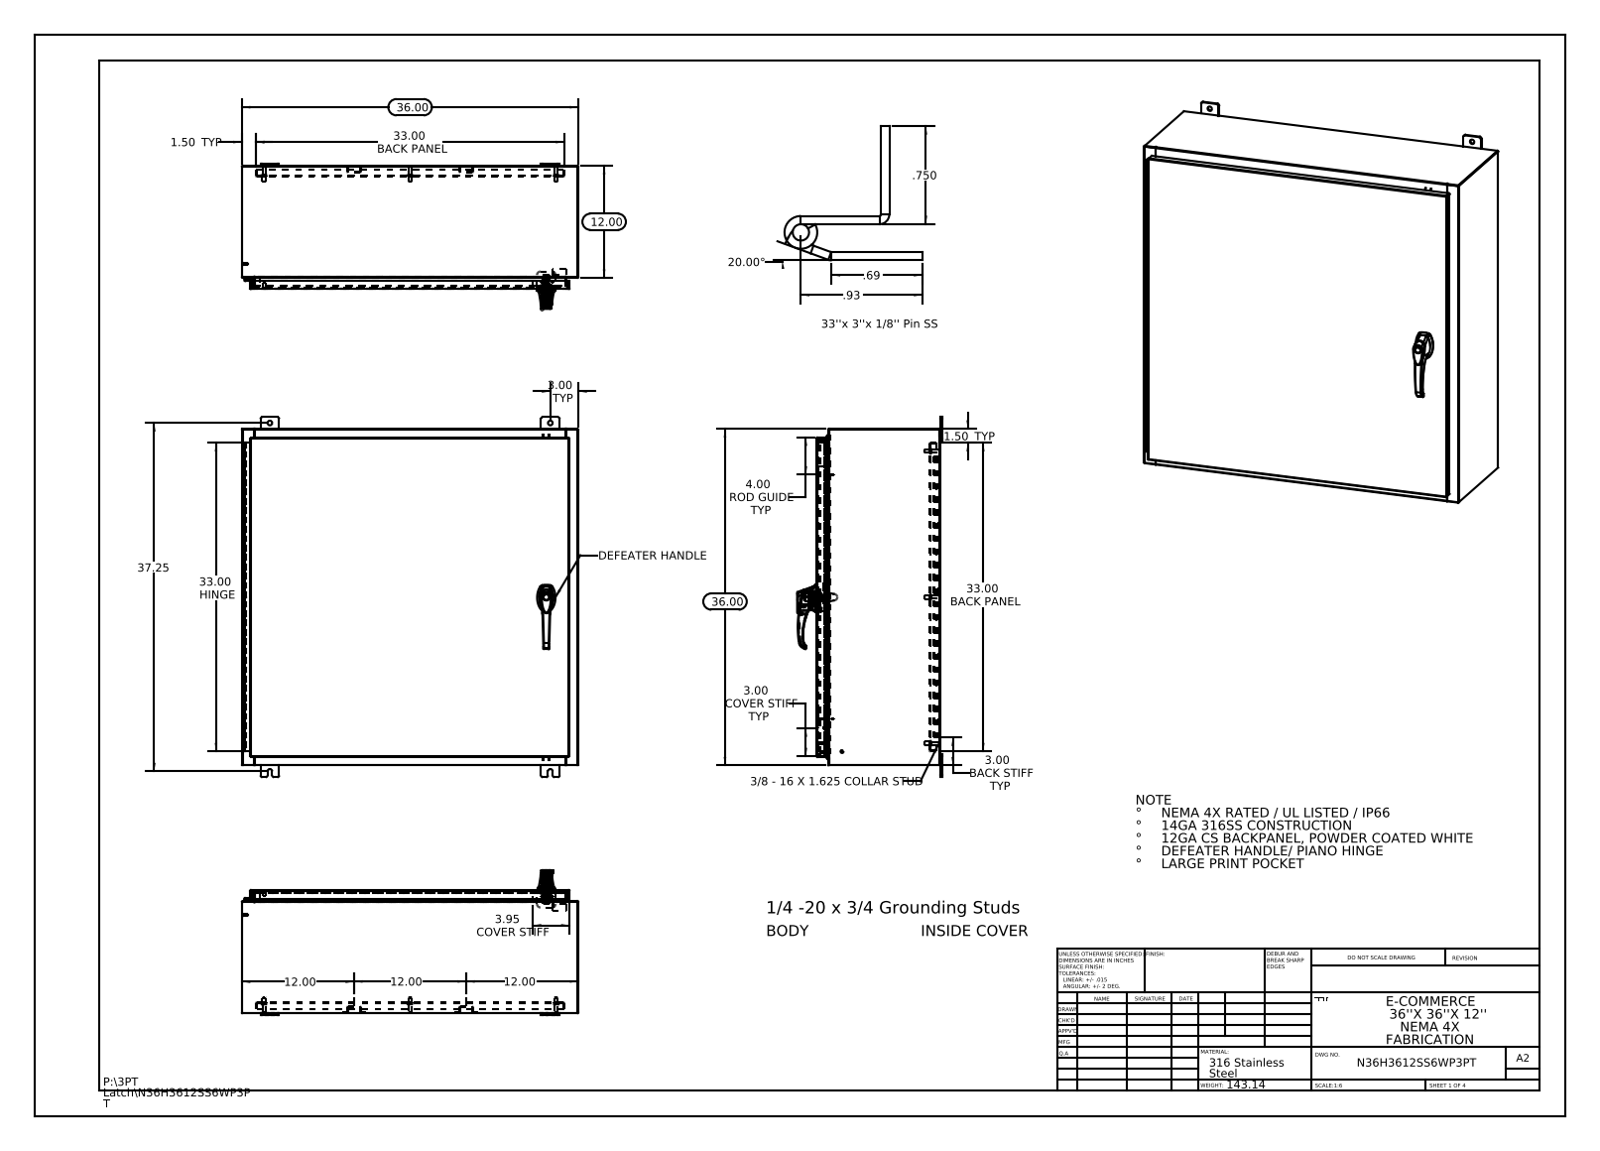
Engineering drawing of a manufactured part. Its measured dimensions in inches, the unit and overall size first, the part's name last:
Units: inches
Overall size (bounding box): 38.5 × 36 × 15.495
Round holes (diameter × count): ⌀0.5 ×12, ⌀0.25 ×10, ⌀0.138 ×3, ⌀0.161 ×3, ⌀0.079 ×2, ⌀0.203 ×2, ⌀0.313 ×2, ⌀0.437 ×2, ⌀0.125 ×1, ⌀0.125 ×1, ⌀0.197 ×1, ⌀0.276 ×1
Round bosses / shafts (diameter × count): ⌀0.625 ×8, ⌀0.375 ×8, ⌀0.33 ×8, ⌀0.157 ×4, ⌀0.14 ×4, ⌀0.315 ×3, ⌀0.236 ×3, ⌀1.181 ×1
Partial cylindrical surfaces — rounded edges, fillets, slot ends (radius × count): R0.118 ×37, R0.013 ×34, R0.006 ×33, R0.088 ×28, R0.19 ×24, R0.039 ×15, R0.028 ×12, R0.008 ×6
Main face-to-face distances: 0.075, 13.126, 35.925, 13.051, 13.201, 0.104, 1, 12.126, 1.075, 12.051
Hole centre spacings: 15.625, 11.363, 13.669, 22.097, 34.939, 34.939, 31.25, 31.25
Volume: 513.8 in³ · Surface area: 12 793 in²
Bodies: 45 solids, 3022 faces (1147 planar, 1137 cylindrical, 738 other)
Part name (STEP PRODUCT): 00005090; 00005310_26163101; N36H3612SS6WP3PT Enclosure Stiffener; NMP-SS-RODGUIDES (+8 more)
STEP written by: SolidWorks 2013 (CONFIG_CONTROL_DESIGN)
